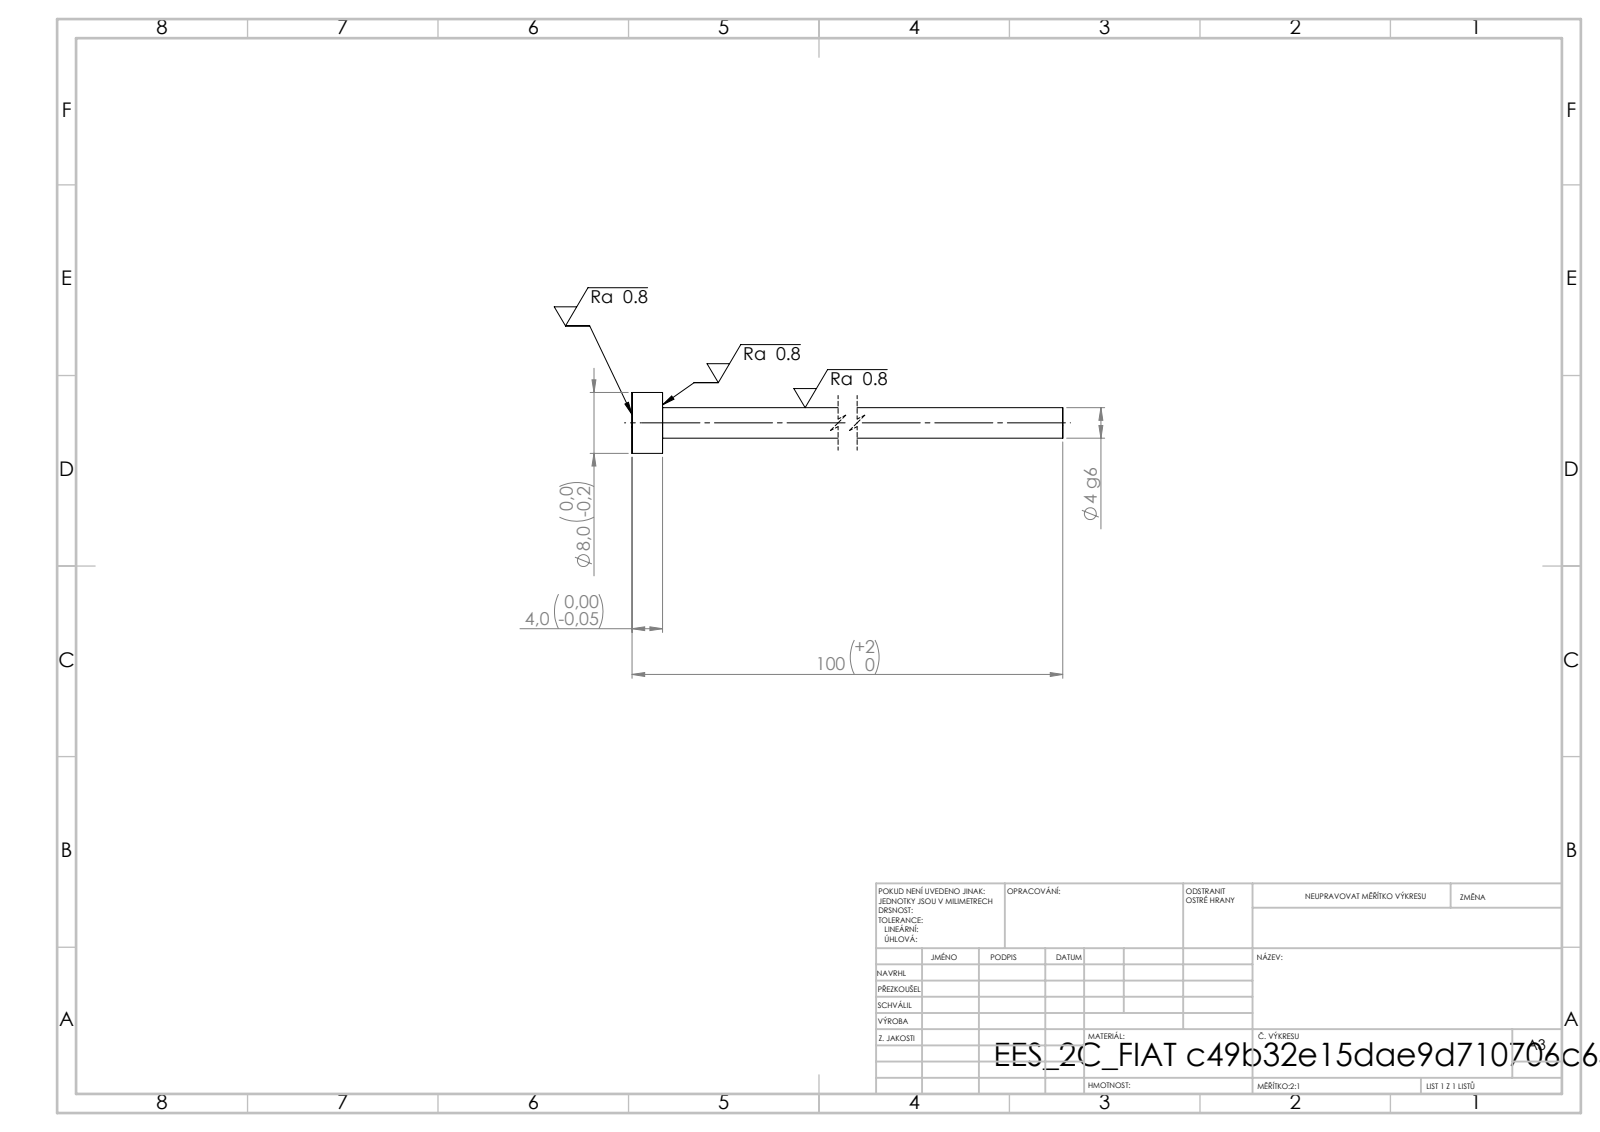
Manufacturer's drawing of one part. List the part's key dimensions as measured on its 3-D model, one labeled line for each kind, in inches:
STEP written by: SolidWorks 2019 (CONFIG_CONTROL_DESIGN)
Units: inches
Bodies: 1 solid, 7 faces (3 planar, 4 cylindrical, 0 other)
Overall size (bounding box): 3.937 × 0.315 × 0.315
Volume: 0.086 in³ · Surface area: 2.181 in²
Round bosses / shafts (diameter × count): ⌀0.315 ×1, ⌀0.157 ×1
Main face-to-face distances: 0.157, 3.937, 3.78
